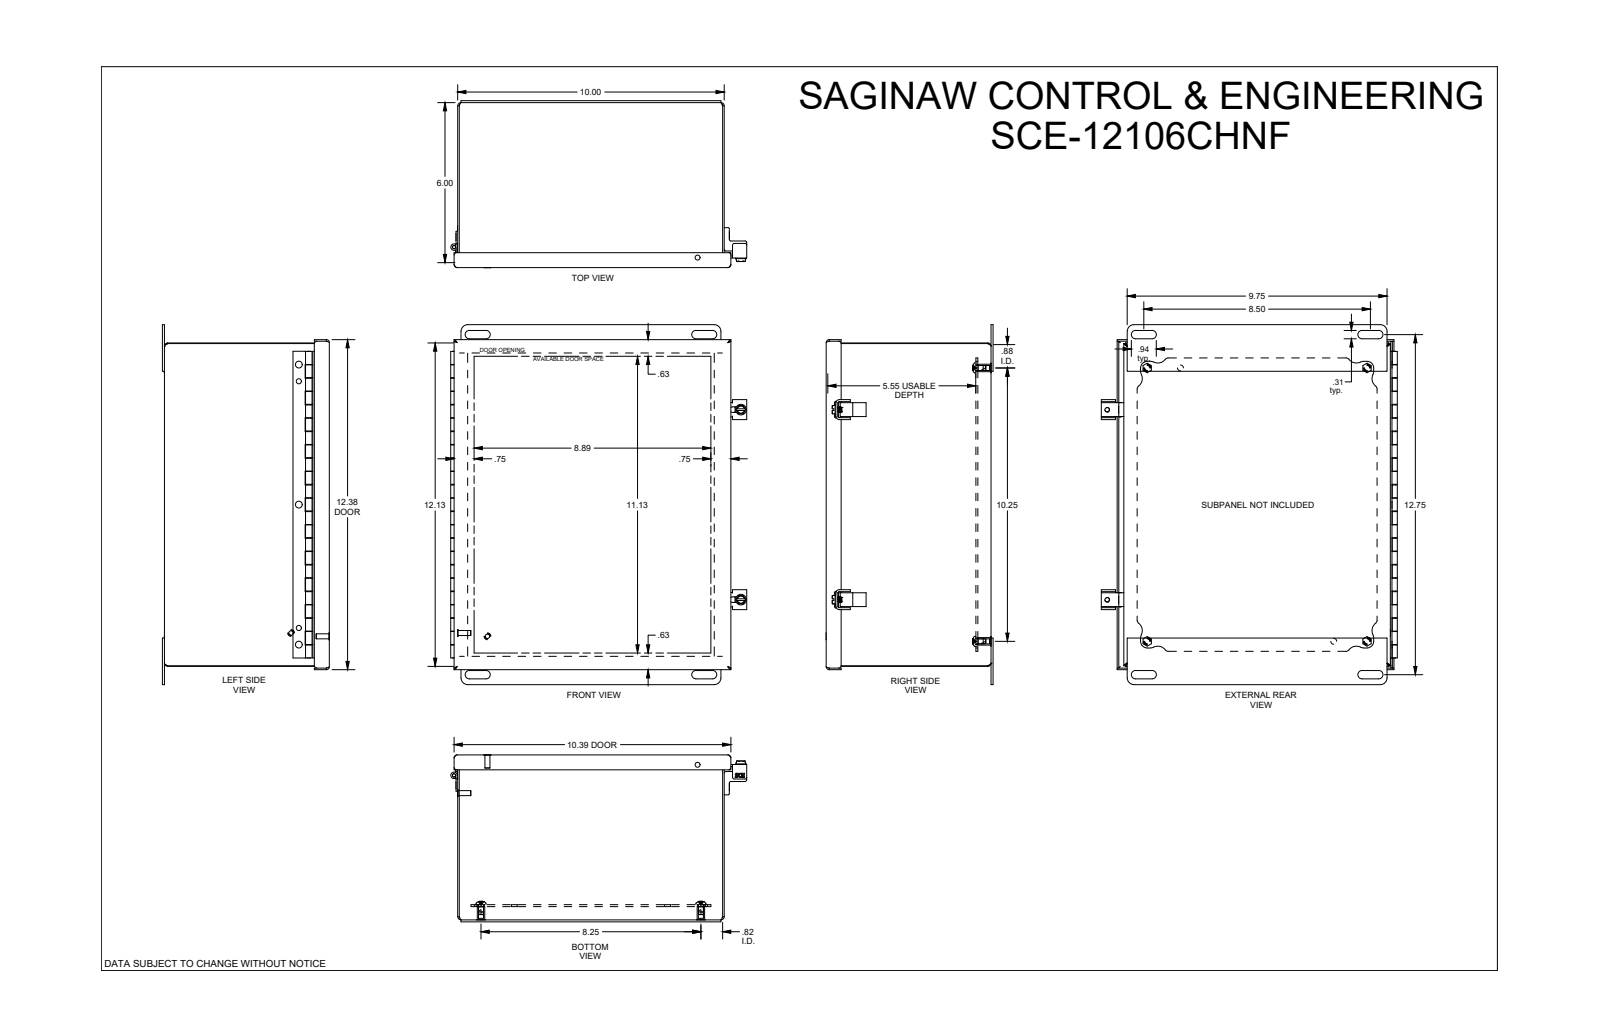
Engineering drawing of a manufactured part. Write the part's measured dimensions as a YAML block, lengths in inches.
part_name: "SCE-12106CHNF"
step_written_by: "SolidWorks 2019 (AUTOMOTIVE_DESIGN)"
units: inches
bodies: {solids: 37, faces: 1244, planar: 548, cylindrical: 349, other: 347}
overall_size: [13.5, 11.104, 6.265]
volume: 47.22
surface_area: 1476
round_holes:
  - {diameter: 0.19, count: 9}
  - {diameter: 0.193, count: 7}
  - {diameter: 0.25, count: 4}
  - {diameter: 0.281, count: 4}
  - {diameter: 0.156, count: 2}
  - {diameter: 0.218, count: 2}
  - {diameter: 0.266, count: 2}
  - {diameter: 0.126, count: 1}
  - {diameter: 0.187, count: 1}
round_bosses_or_shafts:
  - {diameter: 0.188, count: 11}
  - {diameter: 0.256, count: 7}
  - {diameter: 0.373, count: 4}
  - {diameter: 0.28, count: 4}
  - {diameter: 0.396, count: 2}
  - {diameter: 0.188, count: 2}
  - {diameter: 0.246, count: 1}
  - {diameter: 0.123, count: 1}
partial_cylinders:
  - {radius: 0.01, count: 76}
  - {radius: 0.06, count: 33}
  - {radius: 0.25, count: 16}
  - {radius: 0.05, count: 8}
  - {radius: 0.125, count: 8}
  - {radius: 0.156, count: 8}
  - {radius: 0.344, count: 8}
  - {radius: 0.027, count: 6}
face_to_face_distances: [0.06, 6.125, 9.94, 6.185, 6.065, 12.065, 0.435, 0.57, 0.51, 5.555]
hole_center_spacings: [13.157, 10.249, 10.25, 8.25, 13.059, 9.875, 9.875, 10.326]
